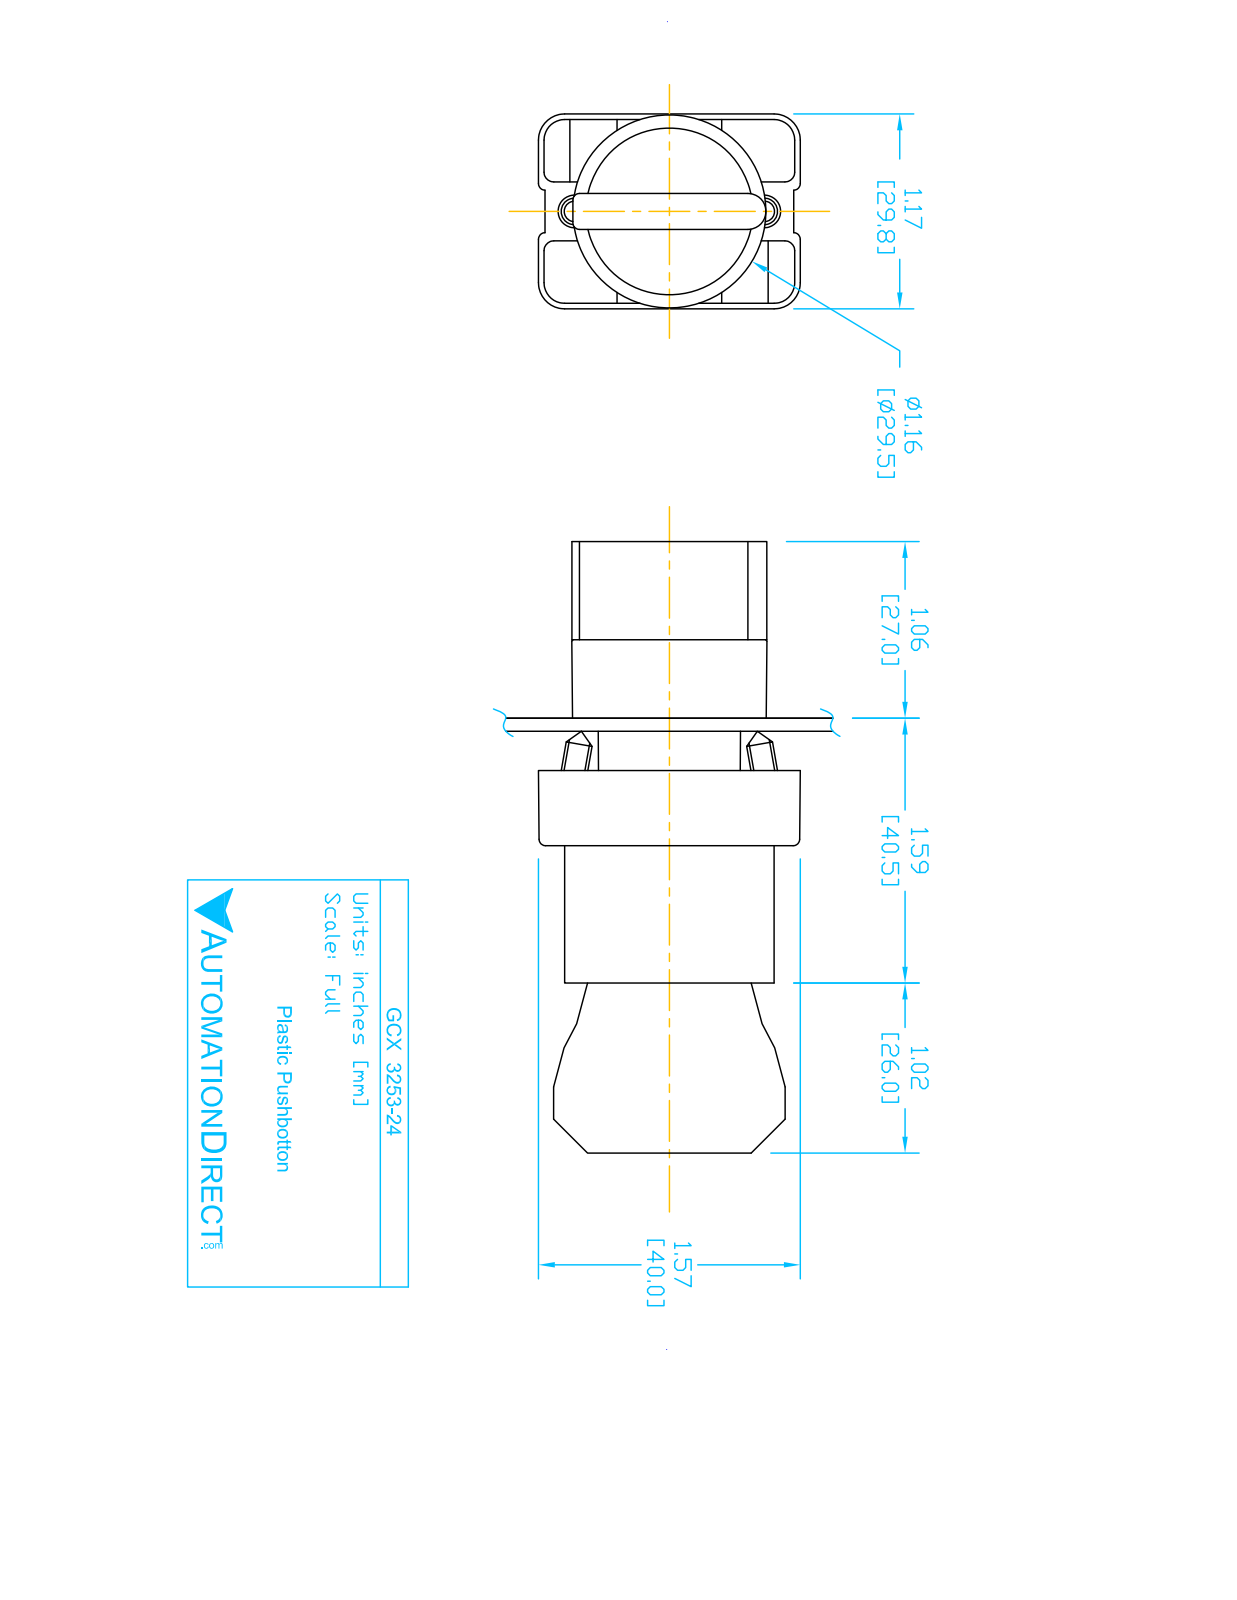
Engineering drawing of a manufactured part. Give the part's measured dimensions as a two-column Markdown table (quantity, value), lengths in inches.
| quantity | value |
| --- | --- |
| part name | ECX1050; ECX3029-2; GCX3253-24; GCX3253 OPERATOR (+1 more) |
| STEP written by | SolidWorks 2016 (AUTOMOTIVE_DESIGN) |
| units | inches |
| bodies | 8 solids, 445 faces (263 planar, 151 cylindrical, 31 other) |
| overall size | 3.653 × 1.581 × 1.177 |
| volume | 2.799 in³ |
| surface area | 39 in² |
| round holes (diameter × count) | 0.079 × 2, 0.124 × 2, 0.13 × 2, 0.087 × 1, 0.197 × 1, 0.469 × 1, 0.878 × 1, 0.888 × 1, 1.024 × 1 |
| round bosses / shafts (diameter × count) | 0.157 × 4, 1.175 × 1, 1.004 × 1, 0.945 × 1, 0.856 × 1, 0.78 × 1, 0.504 × 1 |
| partial cylindrical surfaces (radius × count) | 0.059 × 24, 0.041 × 12, 0.124 × 12, 0.157 × 12, 0.039 × 9, 0.128 × 2, 0.02 × 1, 0.063 × 1 |
| main face-to-face distances | 0.827, 2.02, 1.193, 0.579, 1.244, 1.171, 0.472, 0.469, 0.031, 0.033 |
| hole center spacings | 0.236, 0.544, 0.472, 0.49 |
